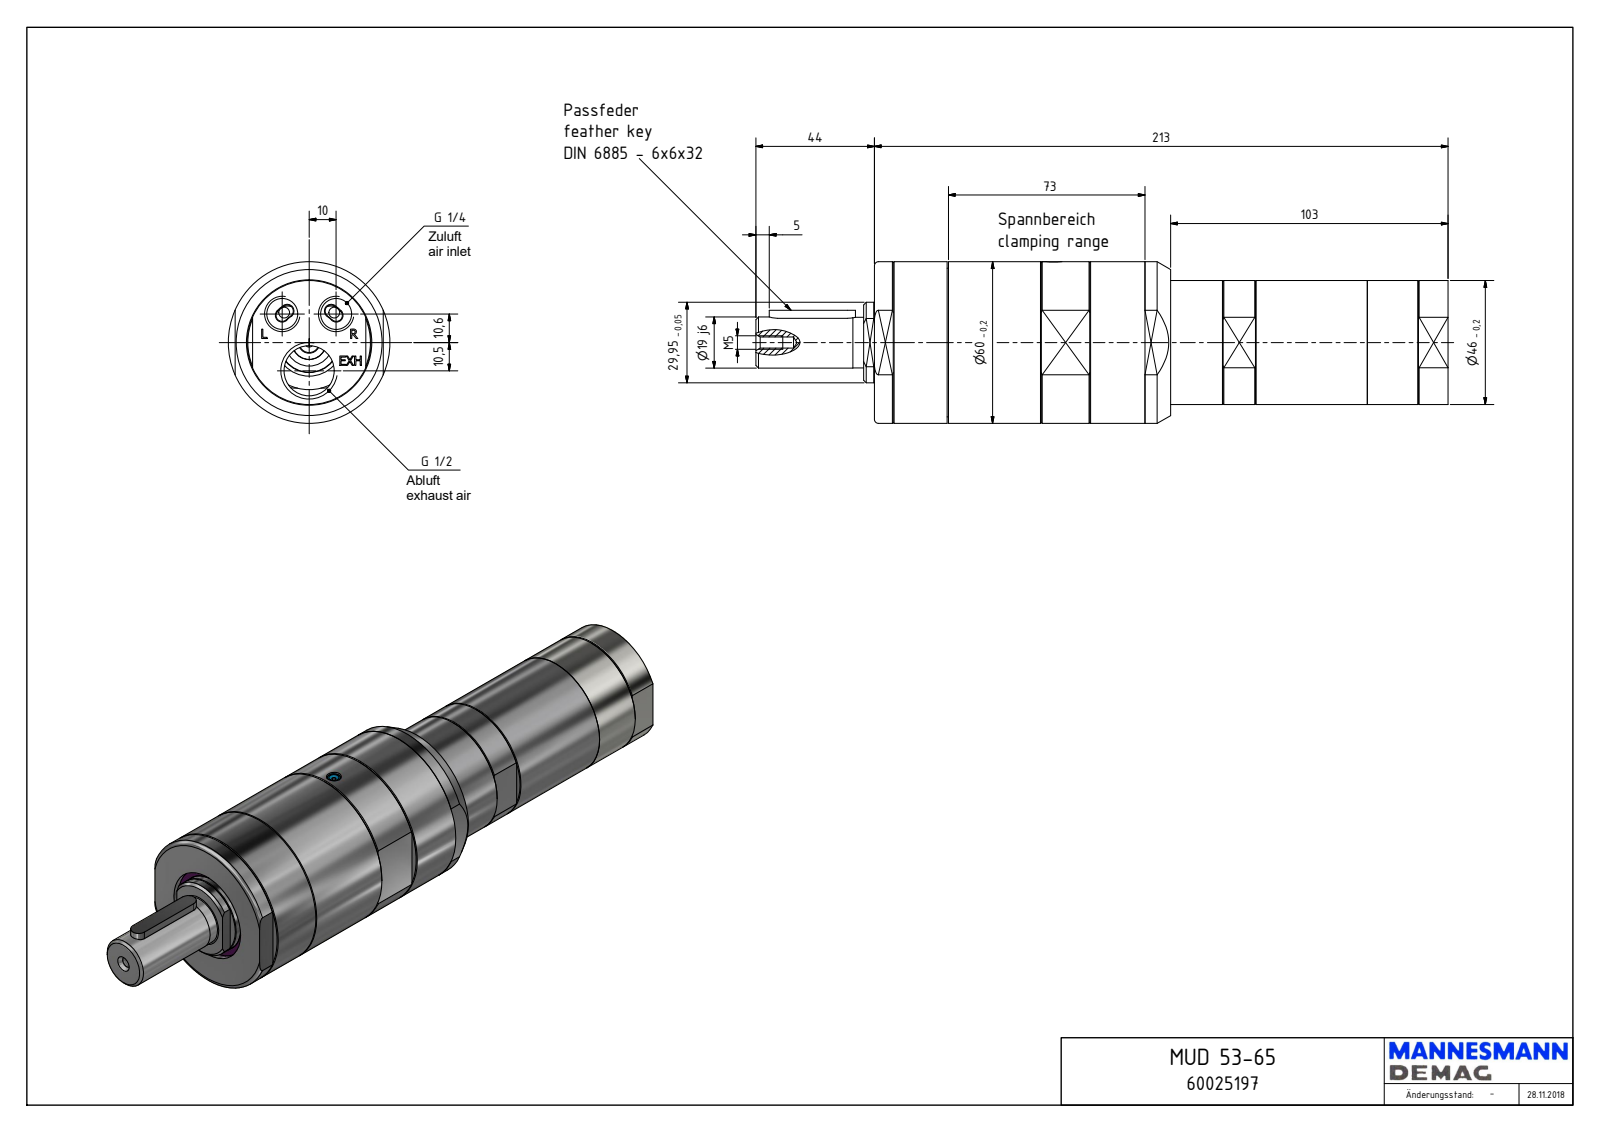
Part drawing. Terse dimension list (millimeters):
name: MUD 53-65_60025197
written by: Autodesk Inventor 2018 (AUTOMOTIVE_DESIGN)
unit: mm
bodies: 1 solid, 218 faces (118 planar, 45 cylindrical, 55 other)
size: 257 × 60 × 60
volume: 484 672 mm³; area: 52 204 mm²
holes: 2× ⌀11.45, 1× ⌀1.55, 1× ⌀4, 1× ⌀4.13, 1× ⌀5.5, 1× ⌀18.63, 1× ⌀35, 1× ⌀36.5, 1× ⌀40, 1× ⌀46.5, 1× ⌀55.38
bosses: 1× ⌀60, 1× ⌀55.18, 1× ⌀46, 1× ⌀29.95, 1× ⌀19, 1× ⌀18.8, 1× ⌀5, 1× ⌀3.6
rounds: 2× R3, 2× R5, 1× R19, 1× R27.16
face distances: 6.5, 213, 48.5, 55, 103, 110, 107.5, 185.5, 6.91, 103.09
hole spacings: 14.57, 23.35, 10.5, 20
